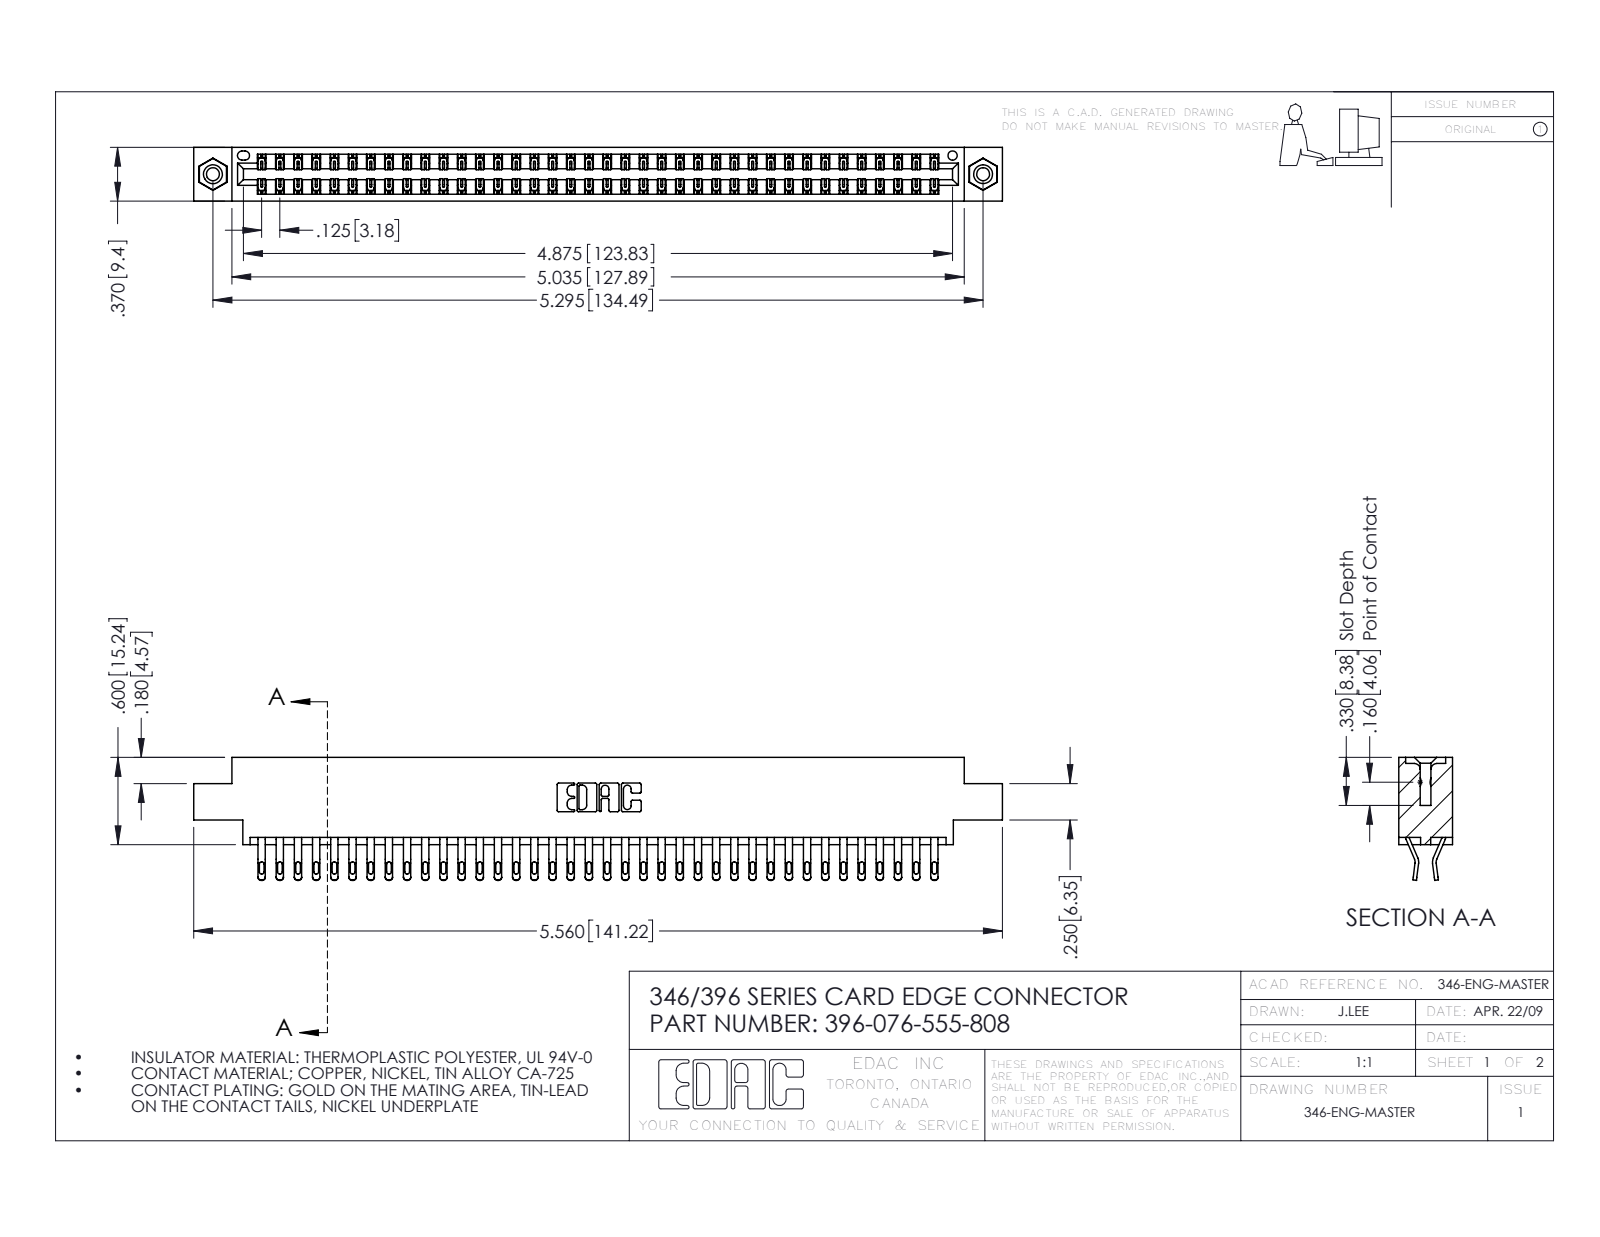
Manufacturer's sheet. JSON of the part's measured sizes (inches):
{"part_name": "345-250-001_345-250-003-102; 345-292-001_555 Tail; 396-076-555-808; 346 Part_0.170 Offset - 0.156 Dia-TI", "step_written_by": "SolidWorks 2016 (CONFIG_CONTROL_DESIGN)", "units": "inches", "bodies": {"solids": 79, "faces": 4594, "planar": 2620, "cylindrical": 1958, "other": 16}, "overall_size": [5.56, 0.845, 0.37], "volume_in3": 0.842, "surface_area_in2": 30.83, "round_holes": [[0.089, 2], [0.125, 2], [0.156, 2], [0.064, 1]], "round_bosses_or_shafts": [[0.155, 2]], "partial_cylinders_radius": [[0.016, 152], [0.02, 152], [0.006, 114], [0.01, 22], [0.007, 6], [0.031, 6], [0.026, 3], [0.01, 2]], "face_to_face_distances": [0.048, 0.322, 0.37, 0.25, 0.025, 0.072, 0.298, 0.275, 0.222, 0.148], "hole_center_spacings": [0.246, 5.086, 5.295]}
